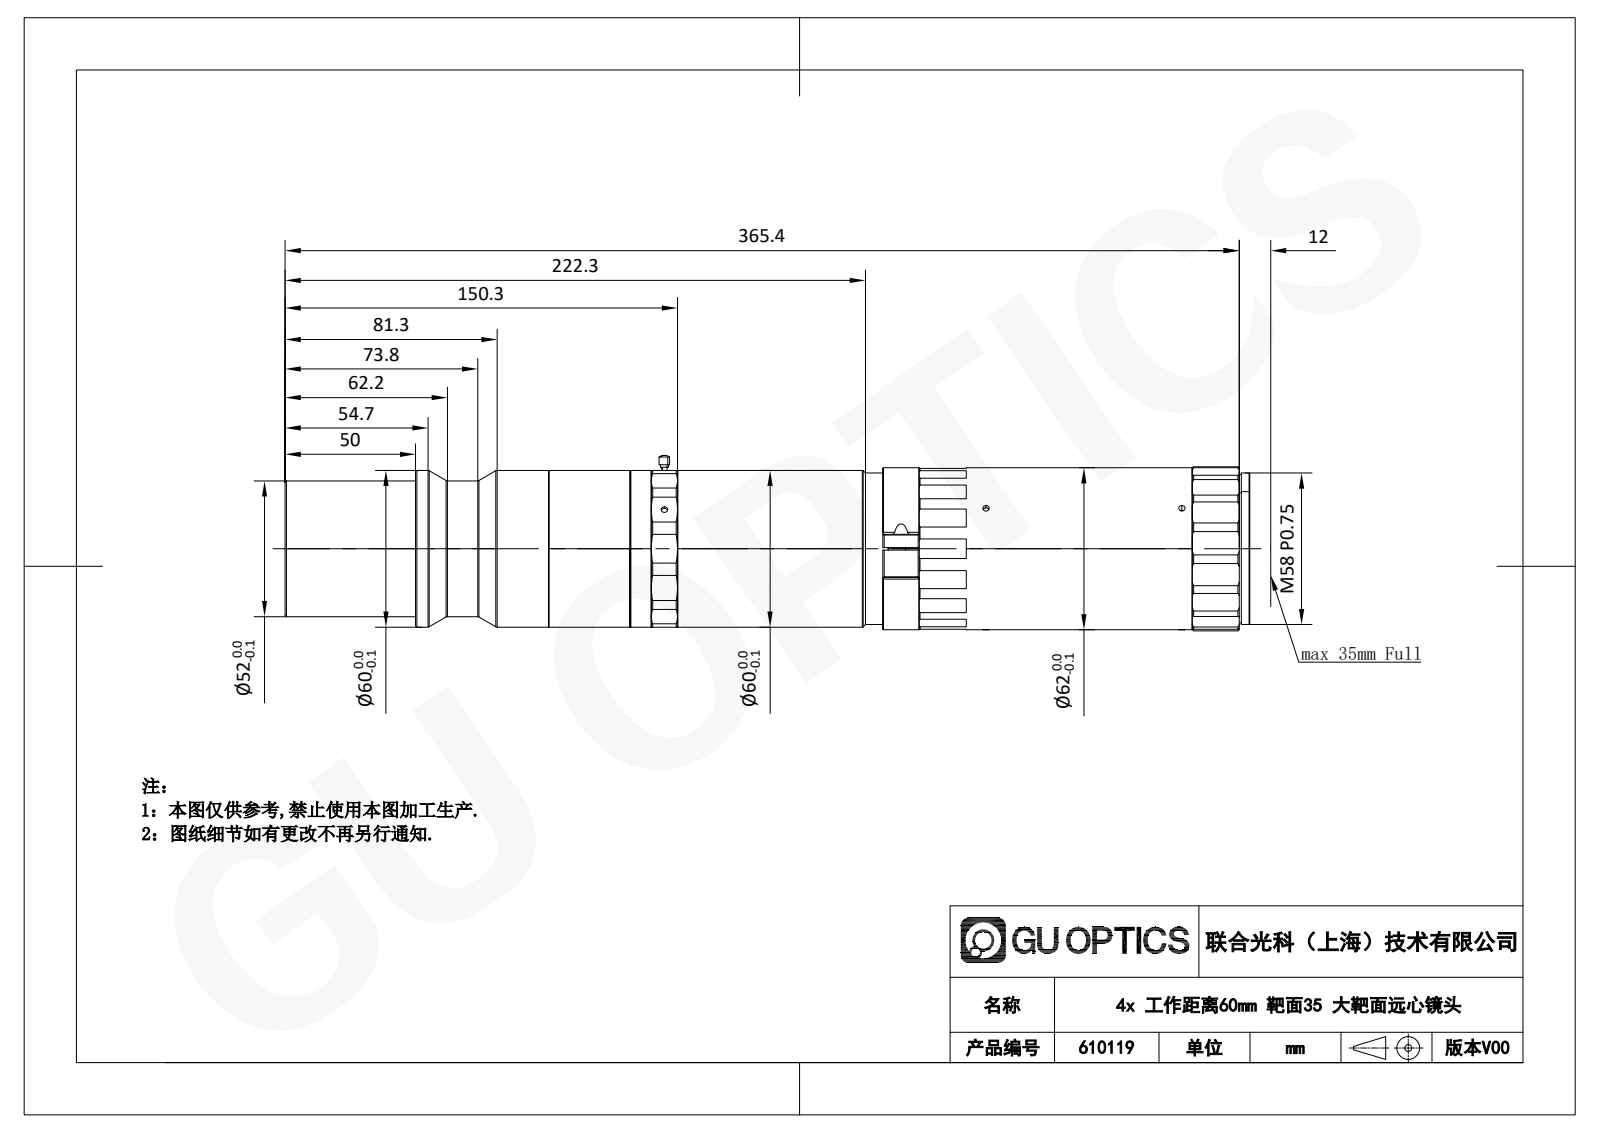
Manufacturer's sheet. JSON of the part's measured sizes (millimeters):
{"part_name": "DTCA35F-11-M58-G-AL", "step_written_by": "SolidWorks 2017 (CONFIG_CONTROL_DESIGN)", "units": "millimeters", "bodies": {"solids": 1, "faces": 406, "planar": 107, "cylindrical": 141, "other": 158}, "overall_size": [369.4, 68.91, 67.19], "volume_mm3": 957209, "surface_area_mm2": 85747, "round_holes": [[2.4, 6], [2.5, 3], [2.2, 1], [3.4, 1], [4.5, 1], [46.5, 1], [47.5, 1], [51.5, 1], [53.5, 1], [55, 1]], "round_bosses_or_shafts": [[62, 1], [60, 1], [58, 1], [56.8, 1], [52, 1], [4, 1], [3, 1], [2, 1]], "partial_cylinders_radius": [[15, 32], [1, 2], [4, 1], [29.3, 1], [29.63, 1], [30.5, 1], [31.5, 1], [37.5, 1]], "face_to_face_distances": [60, 215.13, 50.97, 315.4, 264.43, 100.27, 49.3, 319.4, 268.43, 219.13], "hole_center_spacings": [75, 123.13, 198.13, 46.67, 96.62, 112.6]}
